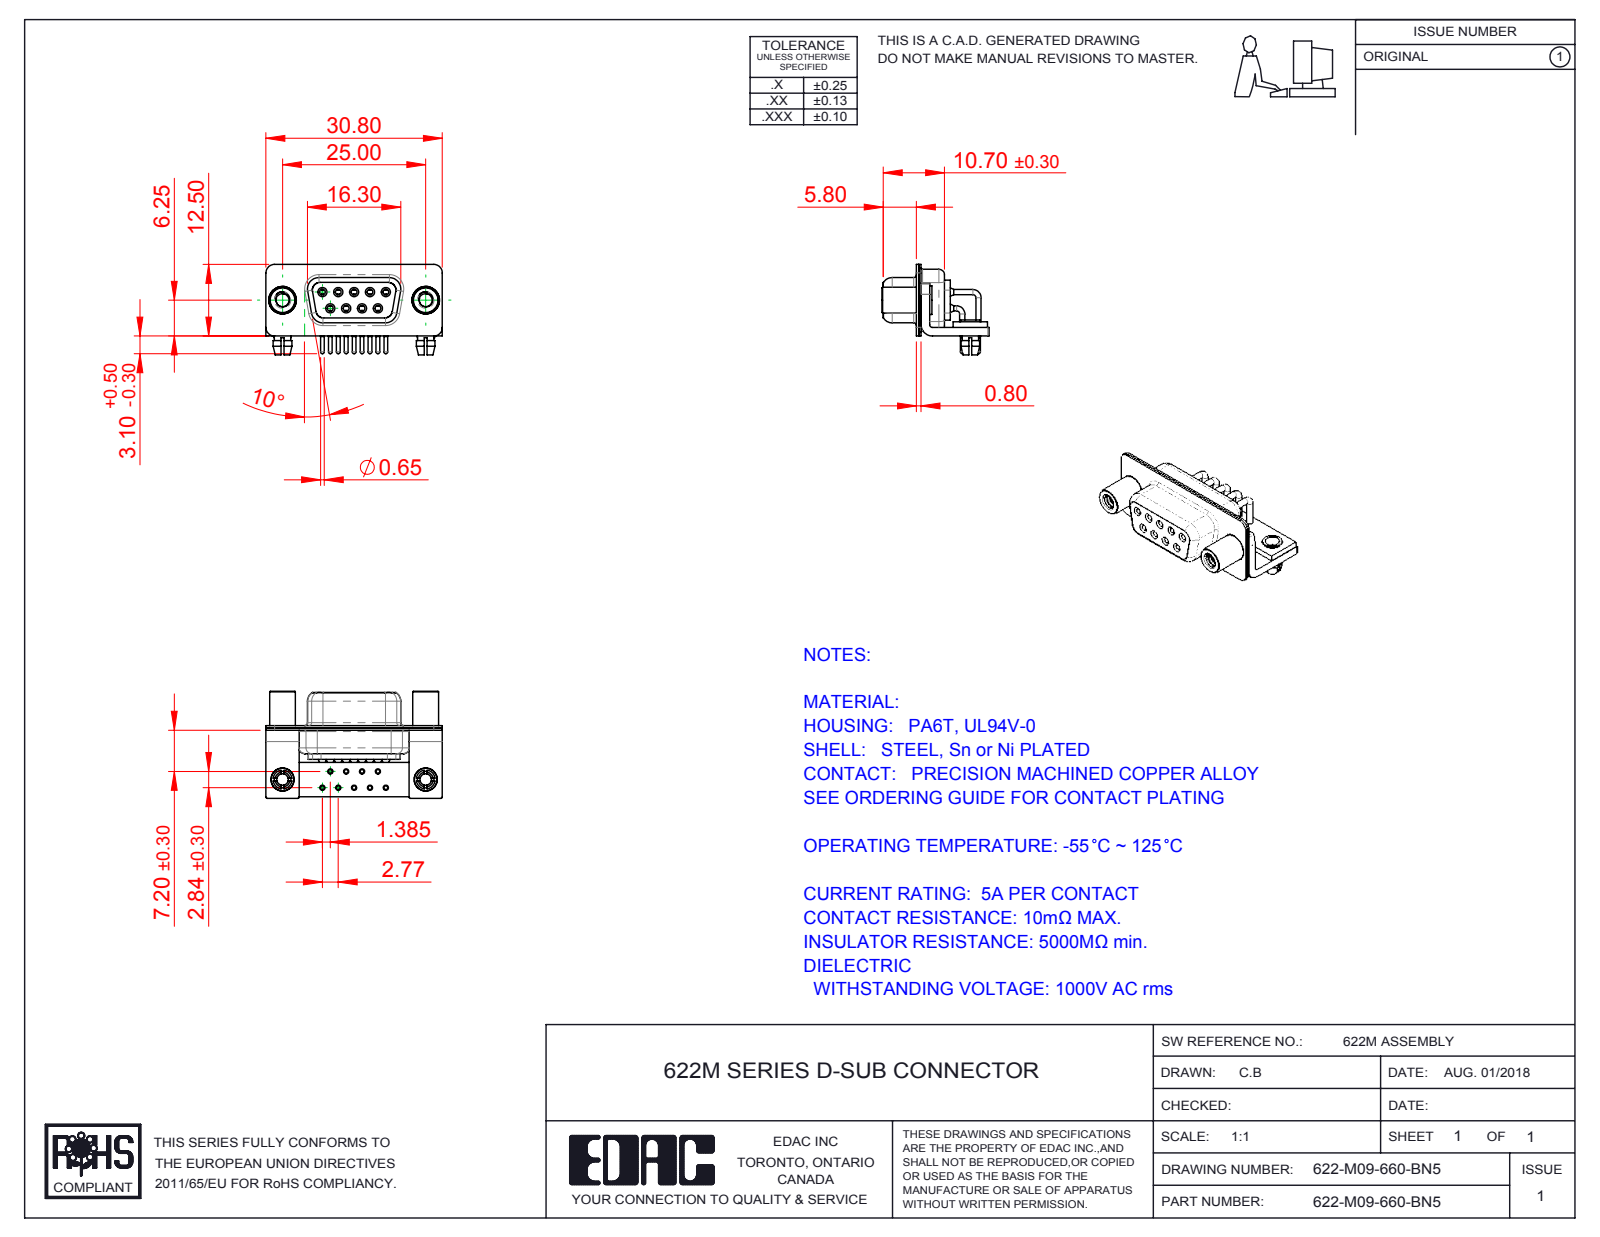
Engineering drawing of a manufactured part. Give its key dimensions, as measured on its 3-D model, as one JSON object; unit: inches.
{"part_name": "622M Stabilizer Bracket; 622M Contact Row 2; 622M Contact Row 1; 622-M09-660-BN5 (+6 more)", "step_written_by": "SolidWorks 2016 (CONFIG_CONTROL_DESIGN)", "units": "inches", "bodies": {"solids": 19, "faces": 966, "planar": 278, "cylindrical": 458, "other": 230}, "overall_size": [1.213, 0.736, 0.622], "volume_in3": 0.141, "surface_area_in2": 9.43, "round_holes": [[0.079, 11], [0.035, 9], [0.039, 9], [0.043, 9], [0.067, 9], [0.071, 9], [0.089, 2], [0.098, 2], [0.126, 2], [0.157, 2], [0.189, 2]], "round_bosses_or_shafts": [[0.063, 9], [0.059, 9], [0.035, 9], [0.026, 9], [0.197, 2], [0.193, 2], [0.177, 2], [0.157, 2]], "partial_cylinders_radius": [[0.01, 16], [0.059, 16], [0.079, 13], [0.053, 8], [0.063, 8], [0.02, 5], [0.024, 4], [0.026, 4]], "face_to_face_distances": [0.016, 0.031, 0.091, 0.059, 0.075, 0.039, 0.368, 0.057, 0.335, 0.352], "hole_center_spacings": [0.124, 0.109, 0.218, 0.198, 0.198, 0.327, 0.294, 0.295]}
